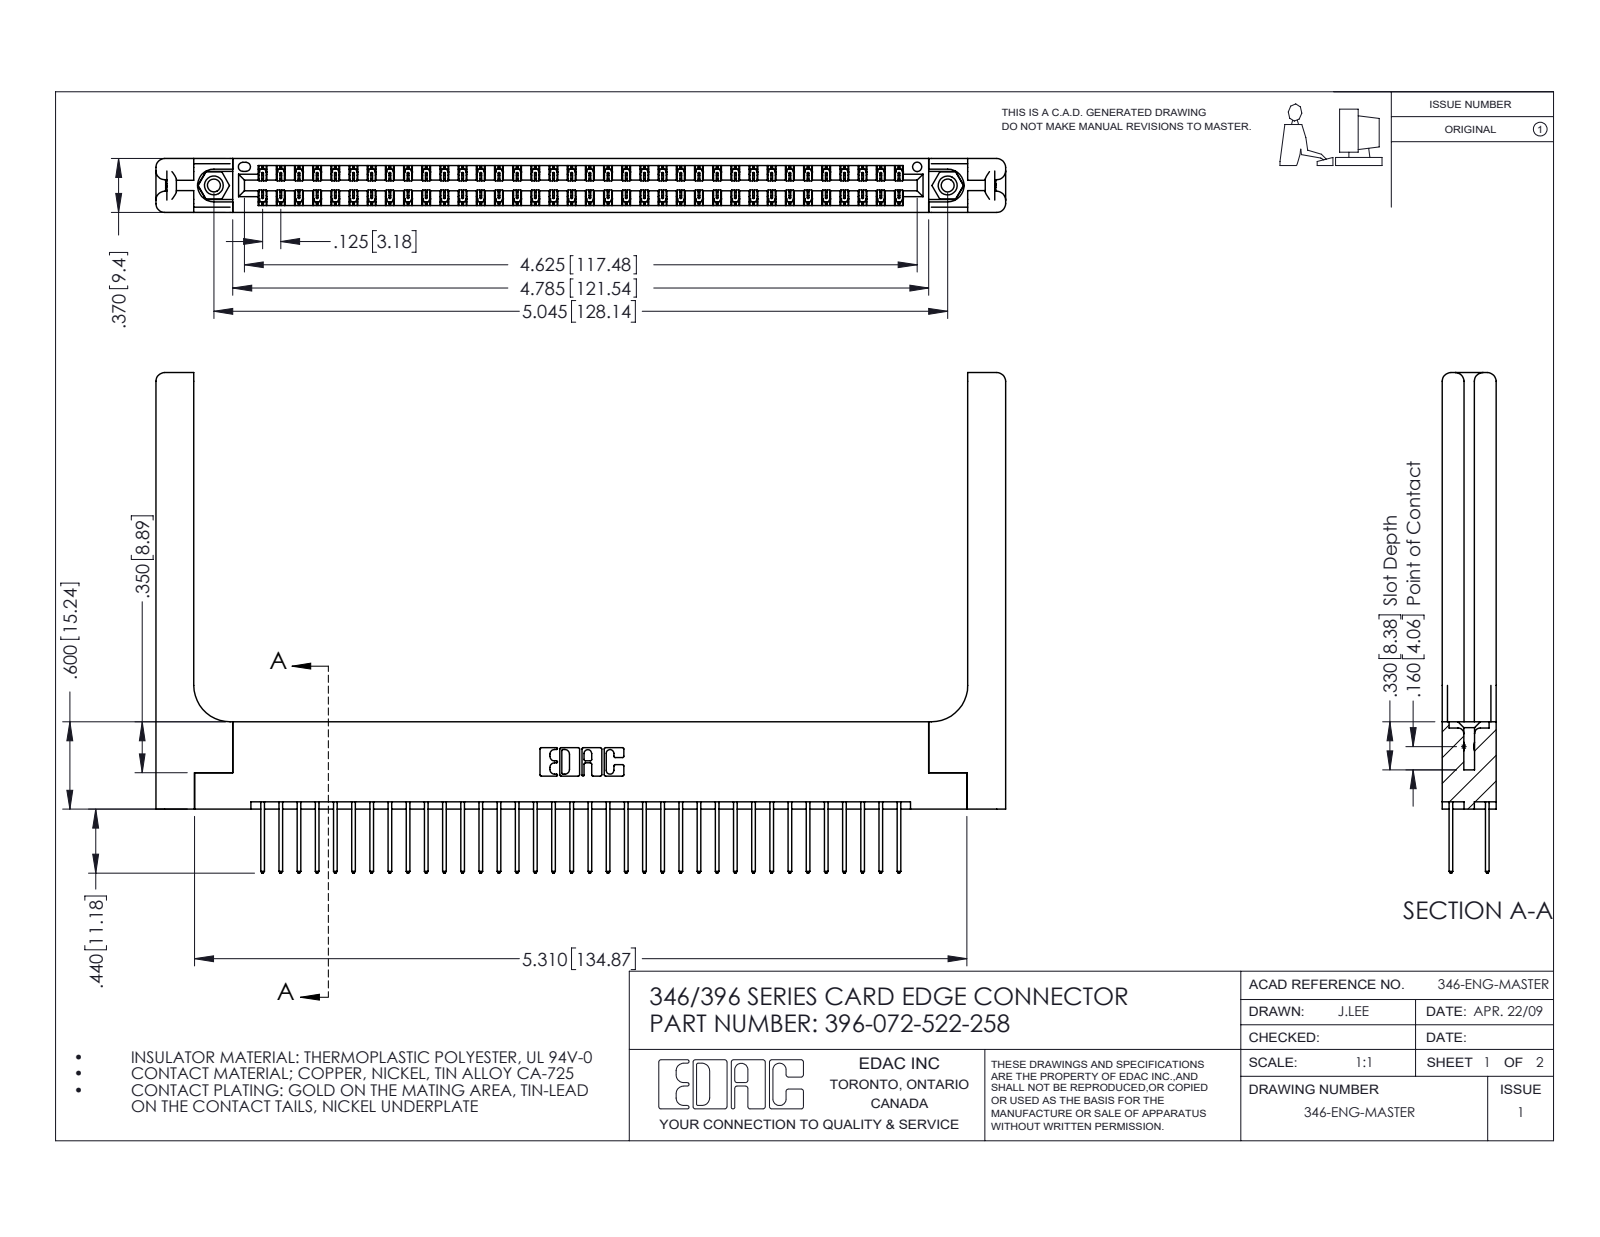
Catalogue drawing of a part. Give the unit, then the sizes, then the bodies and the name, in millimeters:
Units: millimetres
Overall size (bounding box): 148.4 × 87.4 × 9.4
Round holes (diameter × count): ⌀2.3 ×2, ⌀3.2 ×2, ⌀4 ×2, ⌀1.6 ×1
Round bosses / shafts (diameter × count): ⌀3.9 ×2
Partial cylindrical surfaces — rounded edges, fillets, slot ends (radius × count): R0.2 ×108, R0.3 ×72, R0.3 ×22, R1.5 ×16, R0.2 ×6, R0.8 ×6, R0.7 ×3, R0.4 ×2
Main face-to-face distances: 1.2, 8.2, 9.4, 1.8, 6.4, 0.6, 7.6, 3.8, 3.8, 7
Hole centre spacings: 6.2, 122.8, 128.1
Volume: 22 110 mm³ · Surface area: 25 810 mm²
Bodies: 77 solids, 4122 faces (2744 planar, 1318 cylindrical, 60 other)
Part name (STEP PRODUCT): 345-250-001_345-250-001-102; 396-072-522-258; 346-220-058_345-220-058; 346 Part_Flush Mounting Lugs - 0.156 Dia-TH (+1 more)
STEP written by: SolidWorks 2016 (CONFIG_CONTROL_DESIGN)
